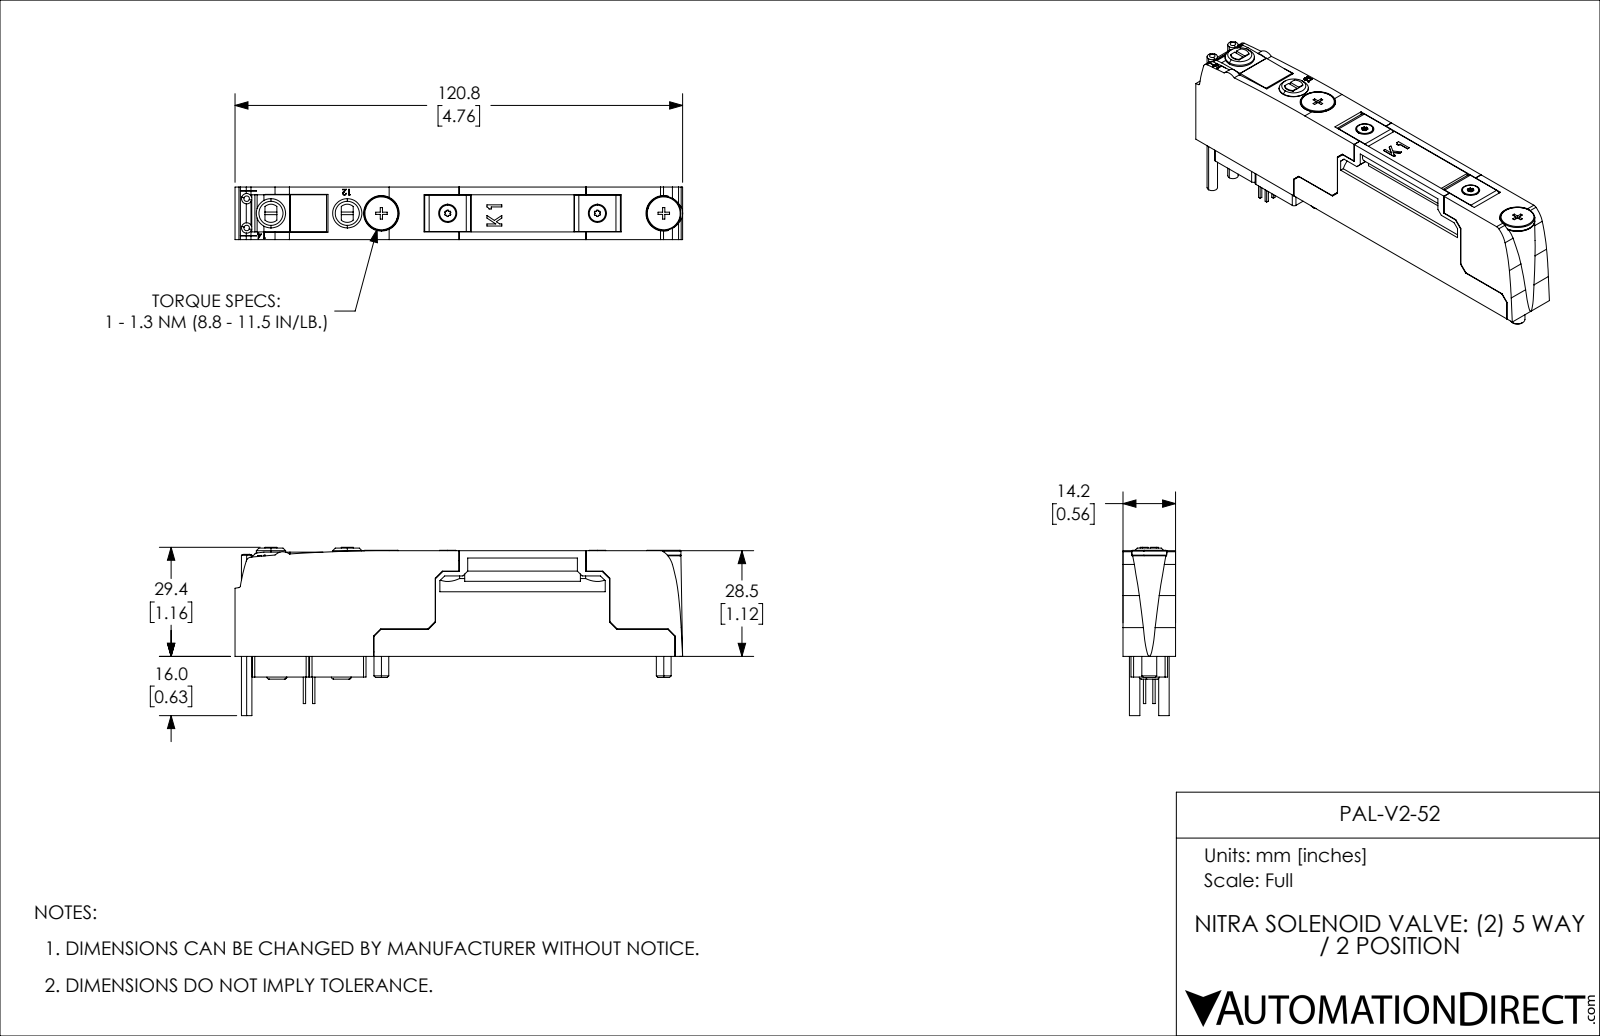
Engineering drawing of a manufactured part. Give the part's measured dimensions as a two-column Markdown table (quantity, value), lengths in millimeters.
| quantity | value |
| --- | --- |
| part name | PAL-V2-52 |
| STEP written by | SolidWorks 2019 (CONFIG_CONTROL_DESIGN) |
| units | millimeters |
| bodies | 1 solid, 561 faces (403 planar, 121 cylindrical, 37 other) |
| overall size | 120.8 × 45.4 × 14.2 |
| volume | 44 729 mm³ |
| surface area | 18 021 mm² |
| round holes (diameter × count) | 3.1 × 2, 4.2 × 2, 9.6 × 1 |
| round bosses / shafts (diameter × count) | 9.3 × 2, 7.9 × 2, 4.4 × 2, 4 × 2, 2.8 × 2 |
| partial cylindrical surfaces (radius × count) | 0.7 × 8, 0.72 × 4, 1.2 × 4, 1.5 × 3, 0.65 × 2, 0.88 × 2, 1.95 × 2, 2.2 × 2 |
| main face-to-face distances | 14.2, 2.1, 12.1, 2.2, 6.4, 28.5, 17.2, 10, 5.6, 21.2 |
| hole center spacings | 10.8, 17.4, 28.2, 76.2, 87, 104.4 |
